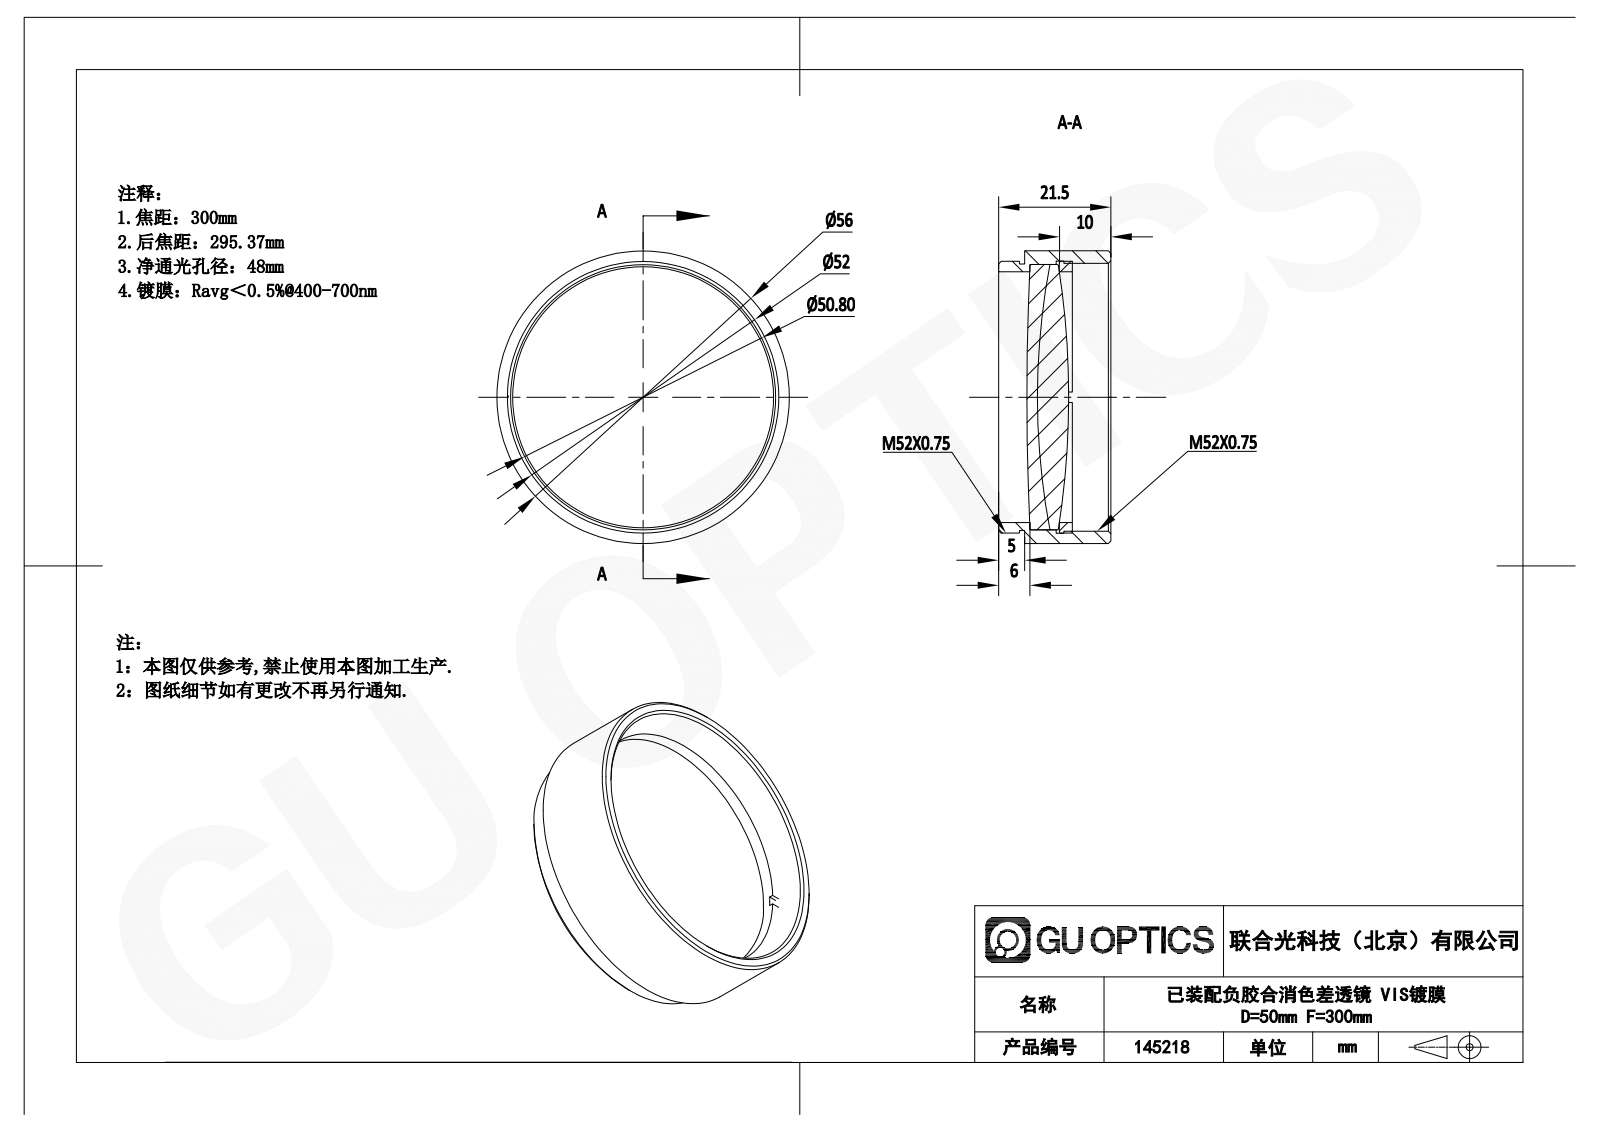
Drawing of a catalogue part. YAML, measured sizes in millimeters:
part_name: "APD-ML50-300-VIS; GL31-050B-300-VIS_Solidworks; M52x0.75ѹȦ"
step_written_by: "SolidWorks 2022 (AUTOMOTIVE_DESIGN)"
units: millimeters
bodies: {solids: 4, faces: 58, planar: 16, cylindrical: 22, other: 20}
overall_size: [56, 56, 21.5]
volume: 22703
surface_area: 18958
round_holes:
  - {diameter: 48, count: 1}
  - {diameter: 51.25, count: 1}
  - {diameter: 52.1, count: 1}
round_bosses_or_shafts:
  - {diameter: 56, count: 1}
  - {diameter: 52, count: 1}
  - {diameter: 51, count: 1}
  - {diameter: 50.8, count: 1}
face_to_face_distances: [5, 6, 9.13, 1, 6.63, 2.5, 11.63, 14.13, 21.5, 16.5]
